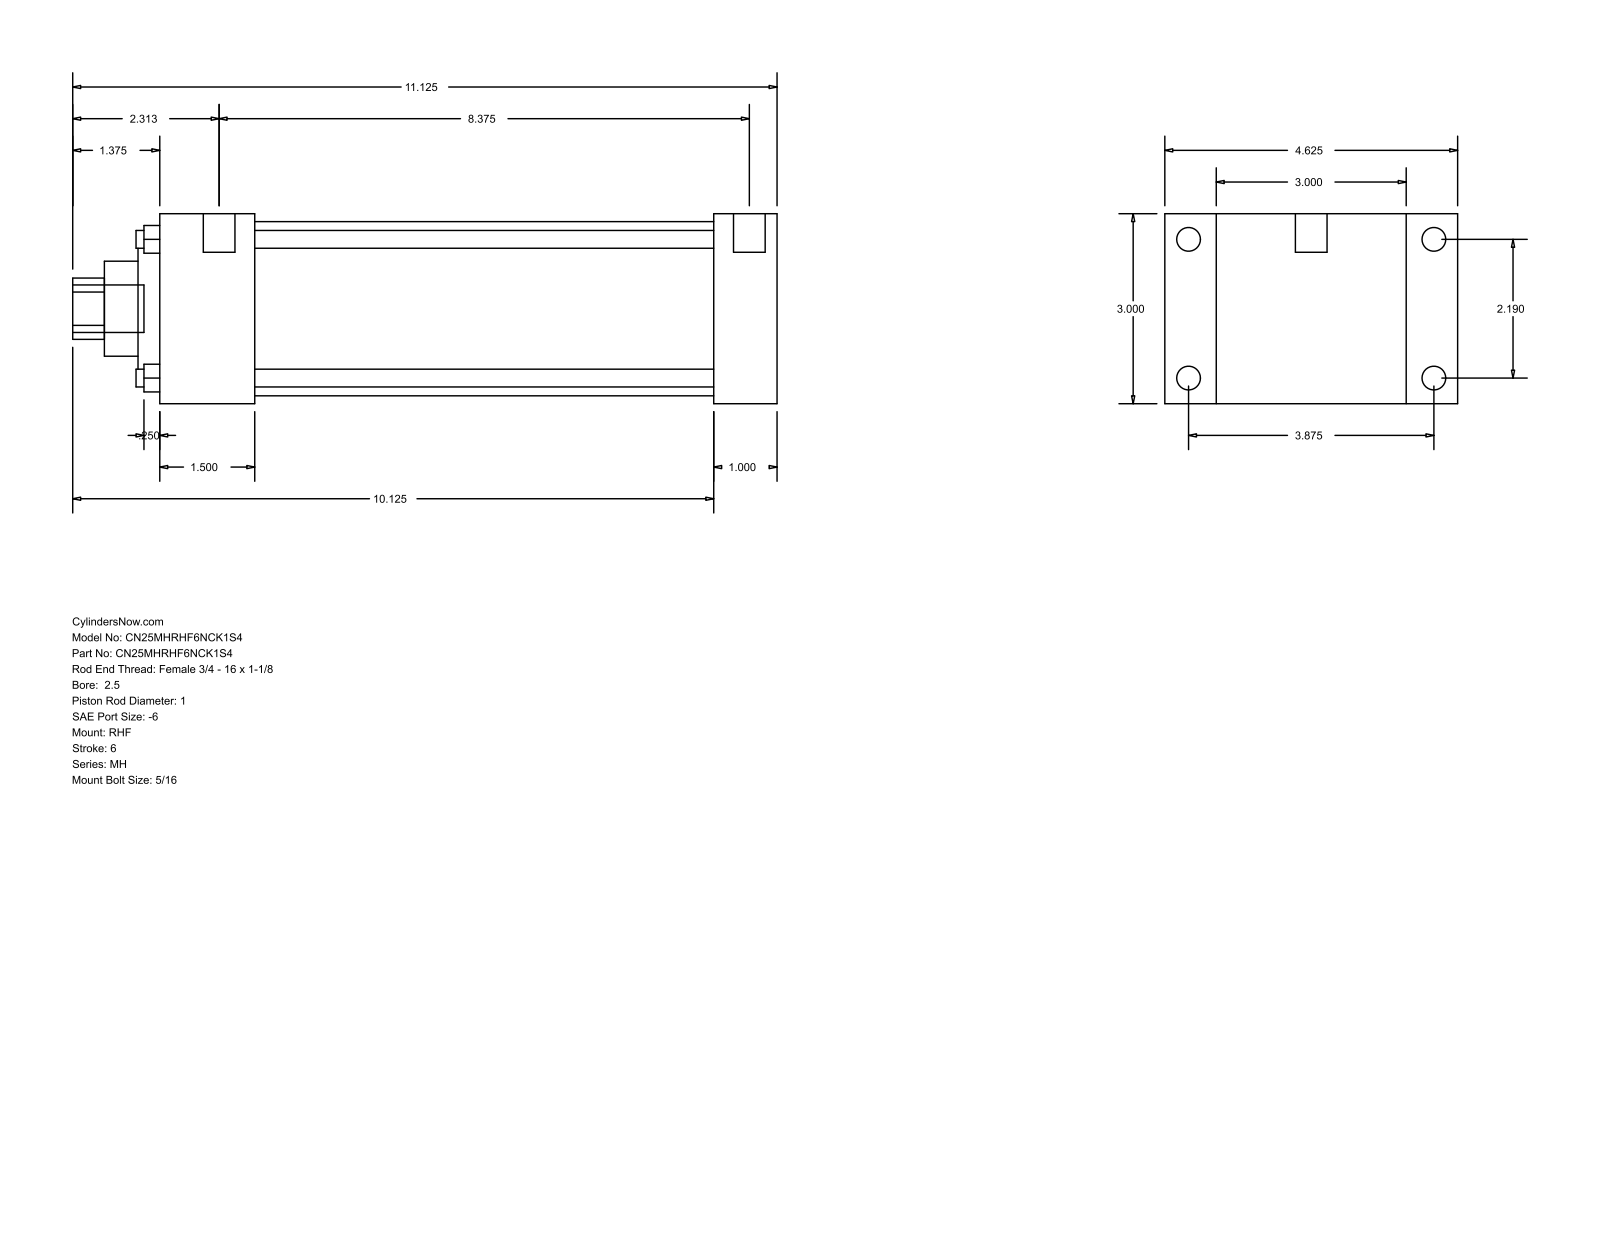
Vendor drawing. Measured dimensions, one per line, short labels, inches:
name: MH_RHF__0250_1
written by: GSSL Pune (CONFIG_CONTROL_DESIGN)
unit: in
bodies: 0 solids, 90 faces (61 planar, 29 cylindrical, 0 other)
size: 11.125 × 4.625 × 3
holes: 4× ⌀0.281, 1× ⌀1, 1× ⌀1.5, 1× ⌀2.375, 1× ⌀2.75
bosses: 4× ⌀0.375, 4× ⌀0.219, 2× ⌀0.5, 1× ⌀0.75
rounds: 1× R0.484
face distances: 3, 1, 0.813, 3.813, 9.75, 8.75, 4.625, 1.5, 7.25, 8.25
hole spacings: 1.548, 2.19, 3.097
